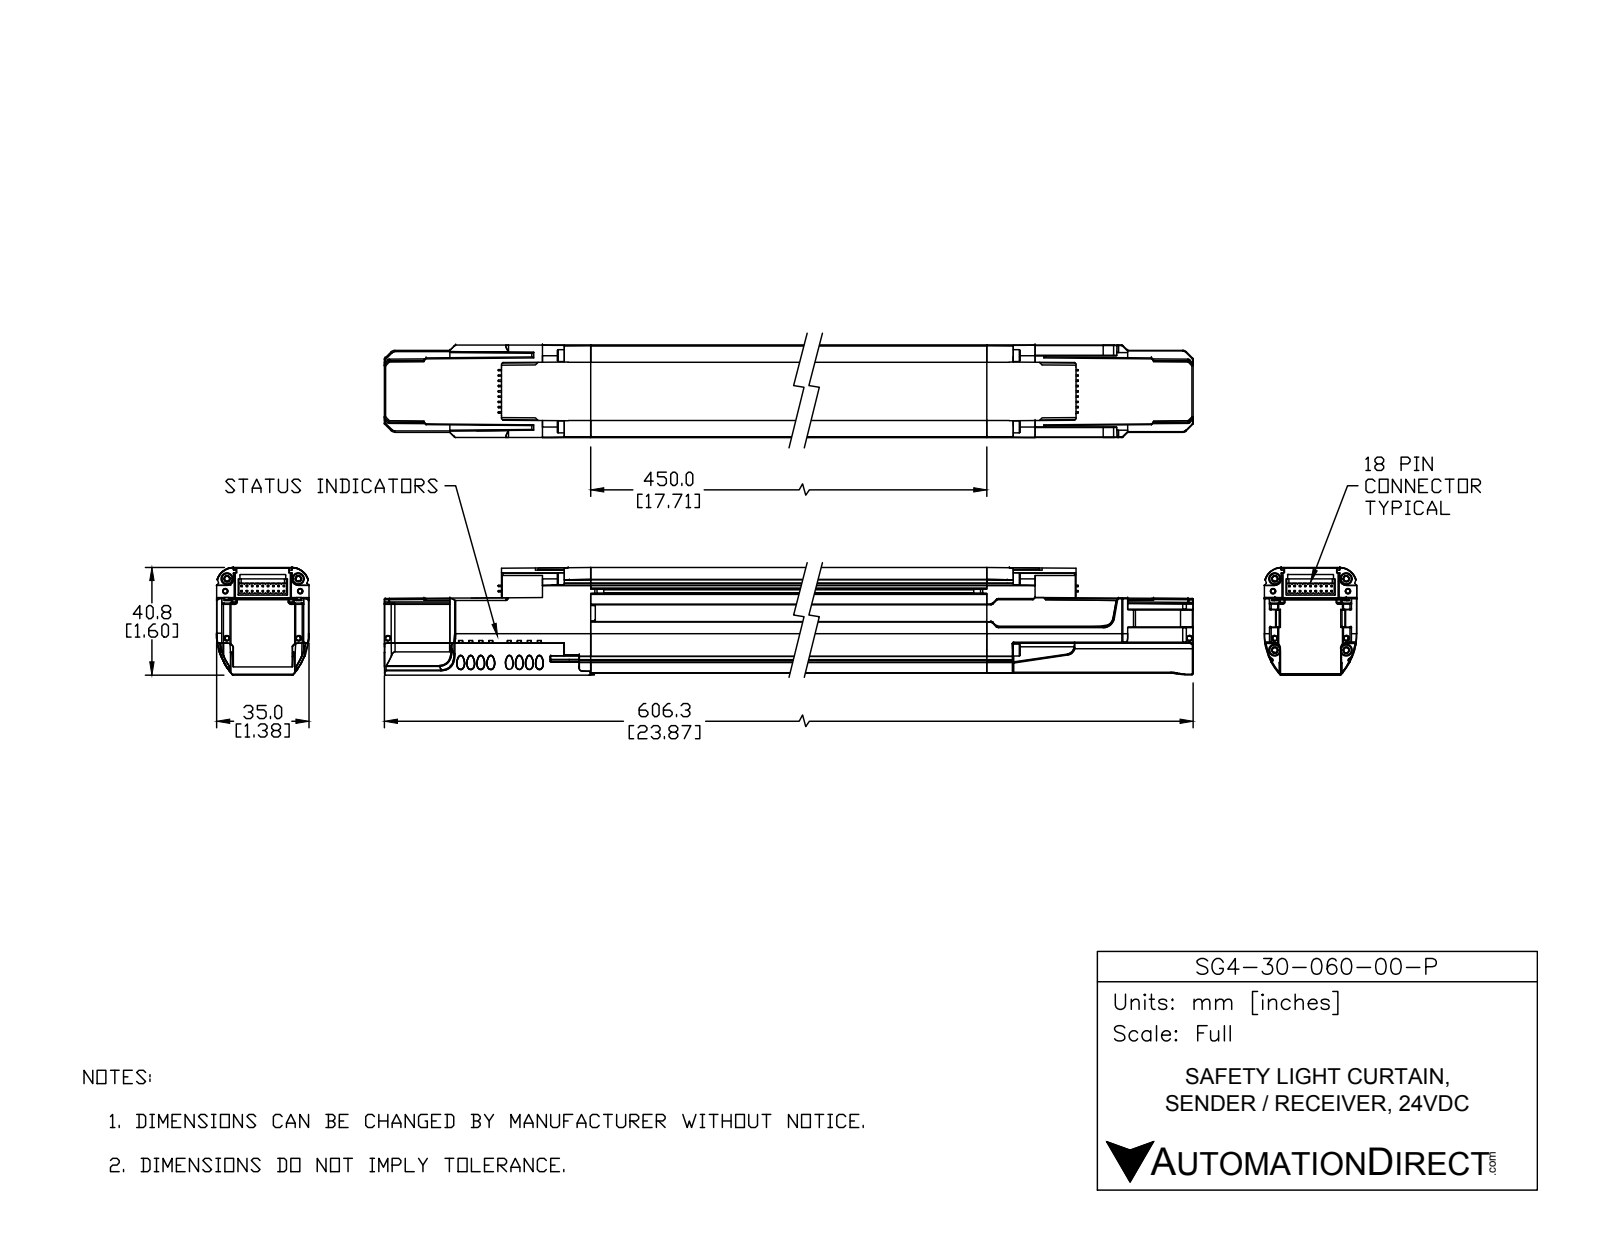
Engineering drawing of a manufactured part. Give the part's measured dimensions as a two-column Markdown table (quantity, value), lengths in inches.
| quantity | value |
| --- | --- |
| part name | SG4-30-060-OO-P |
| STEP written by | SolidWorks 2017 (AUTOMOTIVE_DESIGN) |
| units | inches |
| bodies | 16 solids, 534 faces (362 planar, 110 cylindrical, 62 other) |
| overall size | 23.863 × 2.58 × 2.023 |
| volume | 44.43 in³ |
| surface area | 259.9 in² |
| round holes (diameter × count) | 0.07 × 6, 0.1 × 4, 0.165 × 4, 0.209 × 4, 0.26 × 4, 0.065 × 1, 0.065 × 1 |
| round bosses / shafts (diameter × count) | 0.394 × 4, 0.197 × 4 |
| partial cylindrical surfaces (radius × count) | 0.106 × 16, 0.118 × 8, 0.1 × 4, 0.11 × 4, 0.08 × 2, 0.12 × 2, 0.123 × 2, 0.125 × 2 |
| main face-to-face distances | 0.06, 0.084, 0.024, 1.49, 1.466, 1.55, 1.057, 0.118, 0.481, 0.985 |
| hole center spacings | 0.569, 16.135, 0.02, 0.204, 0.207, 0.207, 0.227, 0.71 |
